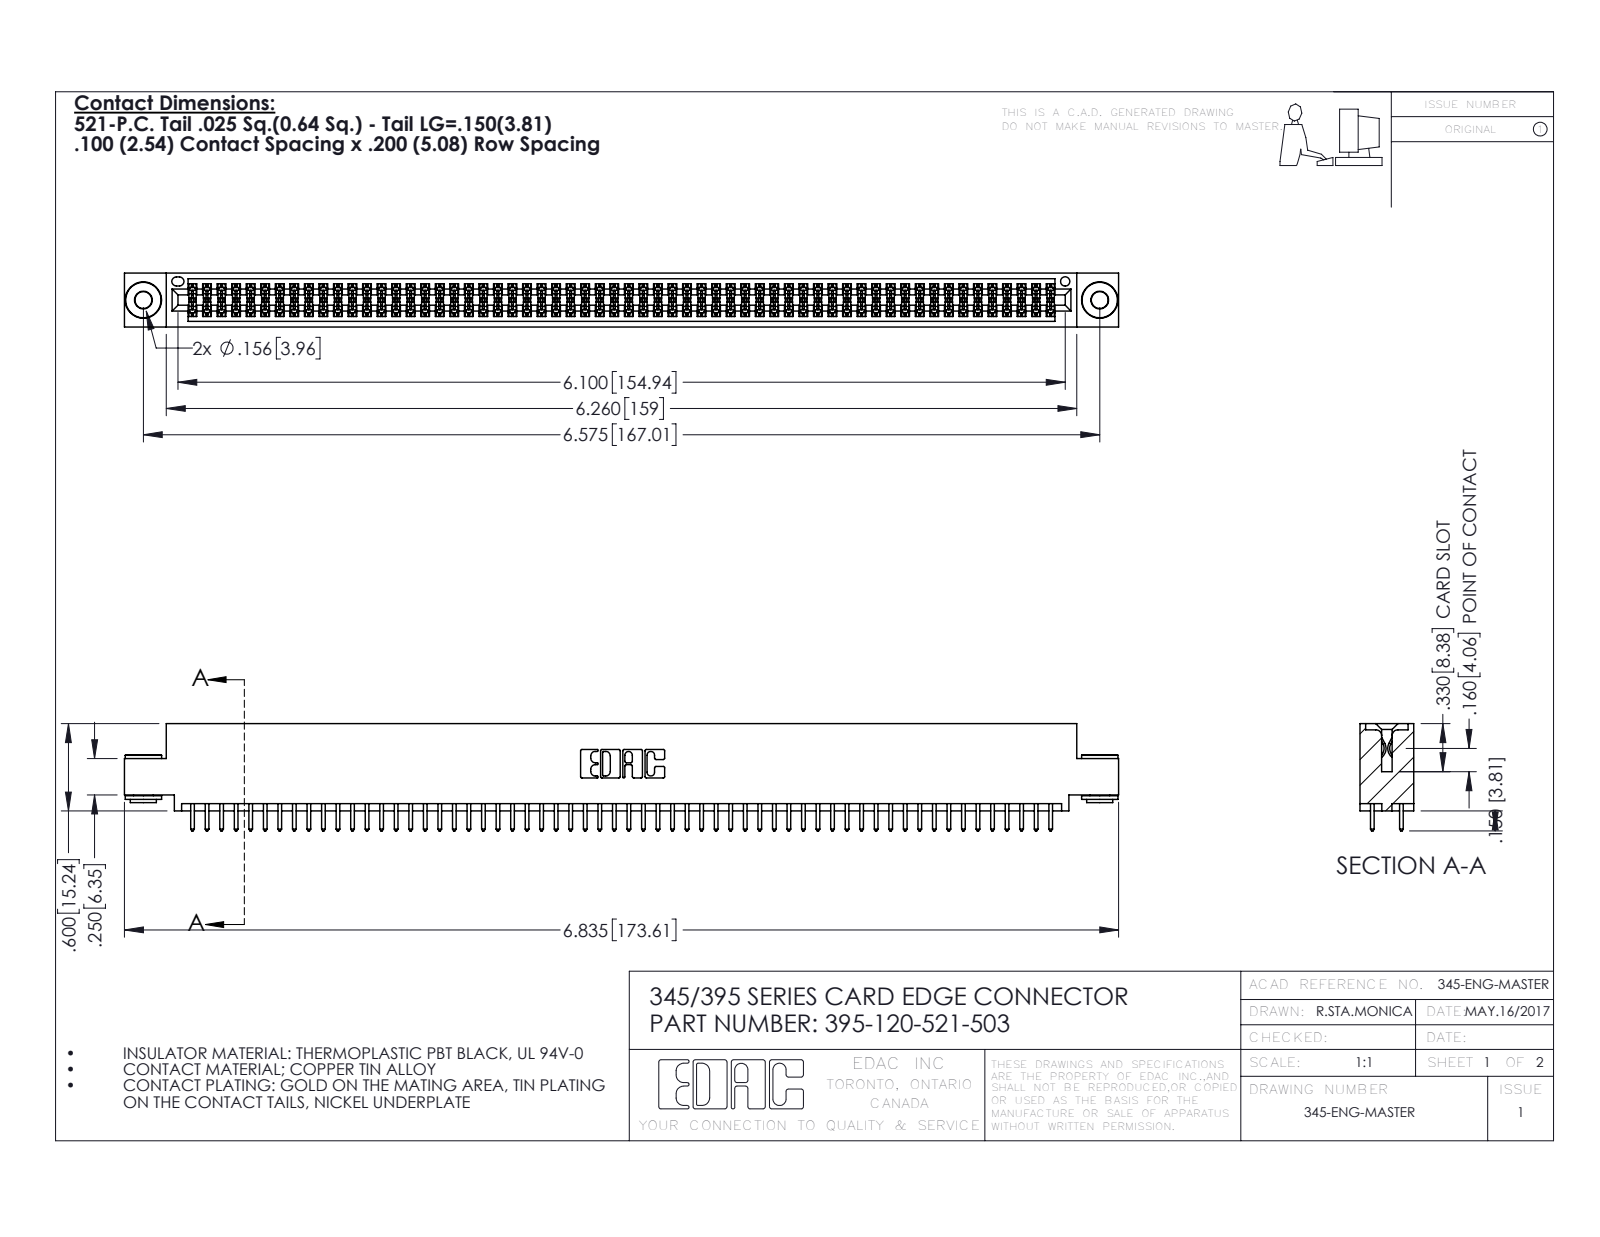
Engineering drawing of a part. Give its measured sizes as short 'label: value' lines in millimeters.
name: 345-250-002_345-250-002-102; 345-292-001_345-293-121; 395-120-521-503; 345 Part_0.110 Offset - 0.156 Dia-TH
written by: SolidWorks 2016 (CONFIG_CONTROL_DESIGN)
unit: mm
bodies: 123 solids, 6168 faces (4054 planar, 2106 cylindrical, 8 other)
size: 173.6 × 18.7 × 9.4
volume: 16 930 mm³; area: 25 350 mm²
holes: 2× ⌀2.9, 2× ⌀4, 1× ⌀1.6
bosses: 2× ⌀6.4, 2× ⌀4.6, 2× ⌀3.5
rounds: 180× R0.2, 120× R0.3, 22× R0.3, 6× R0.2, 6× R0.8, 3× R0.7, 2× R0.4, 2× R0.5
face distances: 1.8, 7.6, 5.1, 0.6, 2.5, 6.9, 9.4, 5.7, 4.4, 3.8
hole spacings: 6.9, 161, 167
